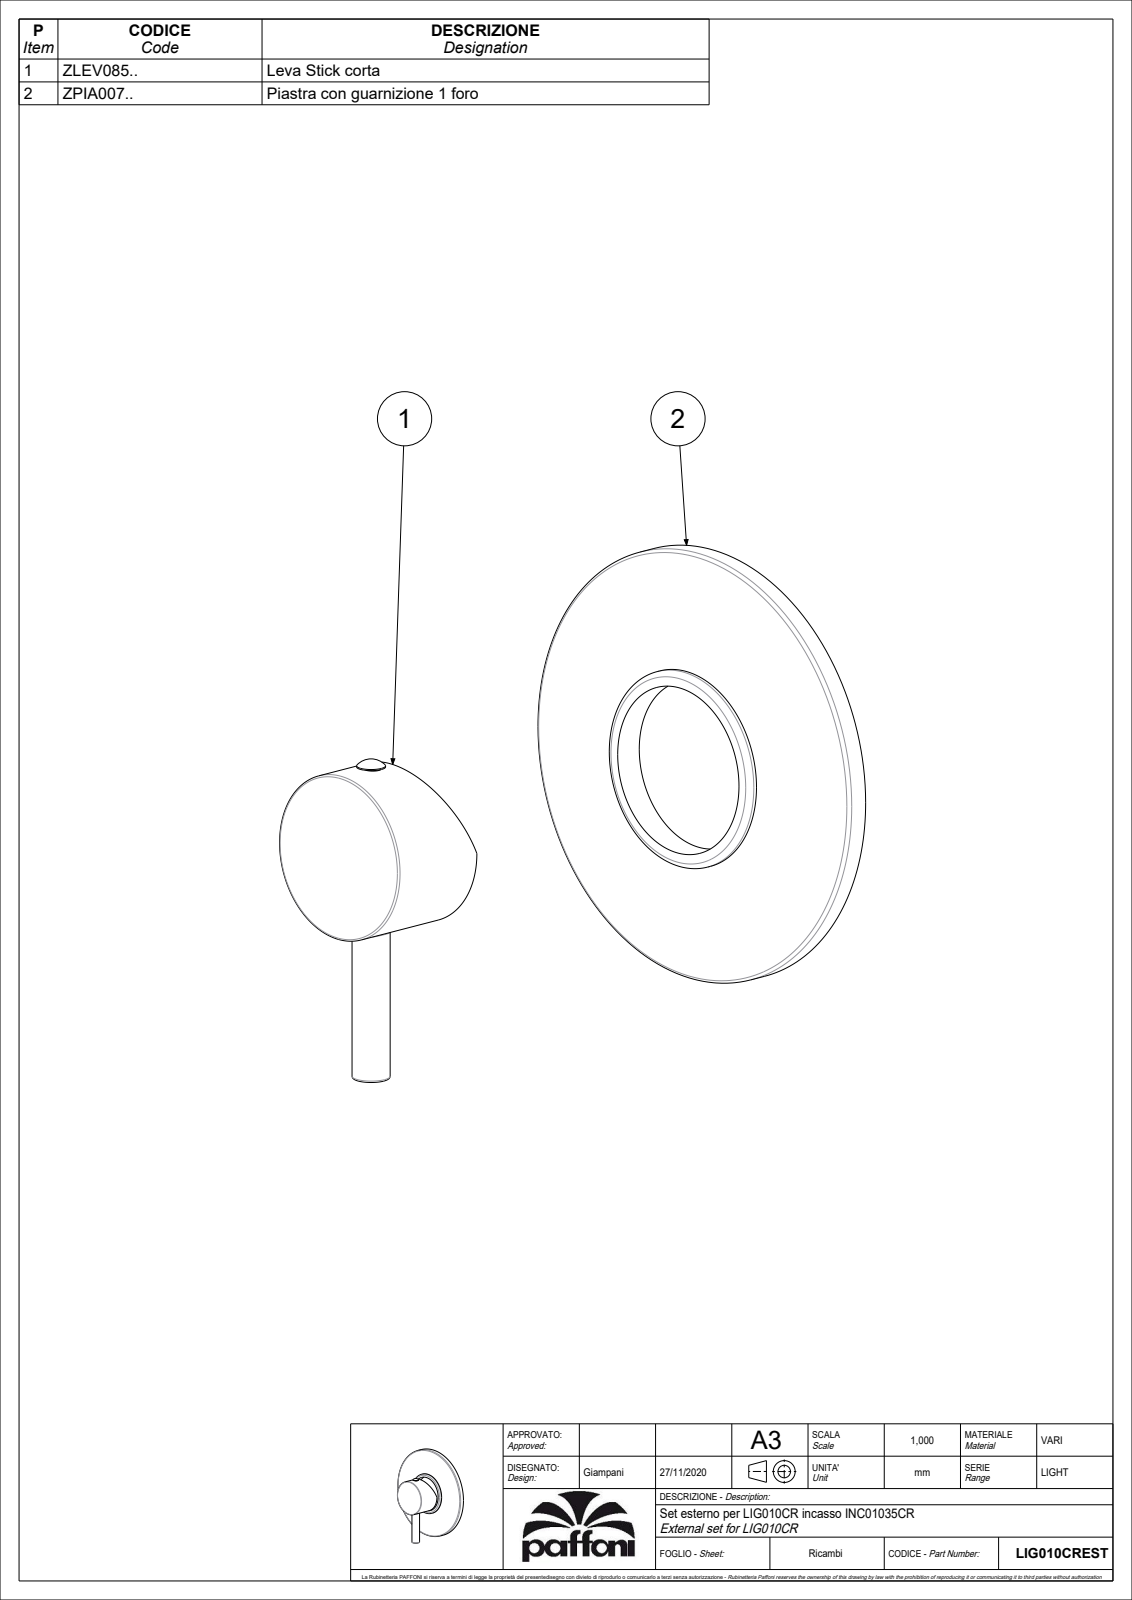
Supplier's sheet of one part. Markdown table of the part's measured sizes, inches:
| quantity | value |
| --- | --- |
| part name | LIG010CREST |
| STEP written by | CREO PARAMETRIC BY PTC INC, 2020044 (CONFIG_CONTROL_DESIGN) |
| units | inches |
| bodies | 2 solids, 191 faces (48 planar, 54 cylindrical, 89 other) |
| overall size | 4.724 × 4.567 × 1.689 |
| volume | 1.672 in³ |
| surface area | 57.6 in² |
| round holes (diameter × count) | 0.118 × 1, 1.772 × 1, 1.969 × 1, 4.488 × 1 |
| round bosses / shafts (diameter × count) | 4.567 × 1, 2.087 × 1, 1.752 × 1, 0.394 × 1, 0.299 × 1, 0.217 × 1, 0.197 × 1 |
| partial cylindrical surfaces (radius × count) | 0.02 × 8 |
| main face-to-face distances | 0.157, 1.063, 0.453, 1.516, 0.098, 0.315, 0.354, 1.161, 0.059, 0.138 |
